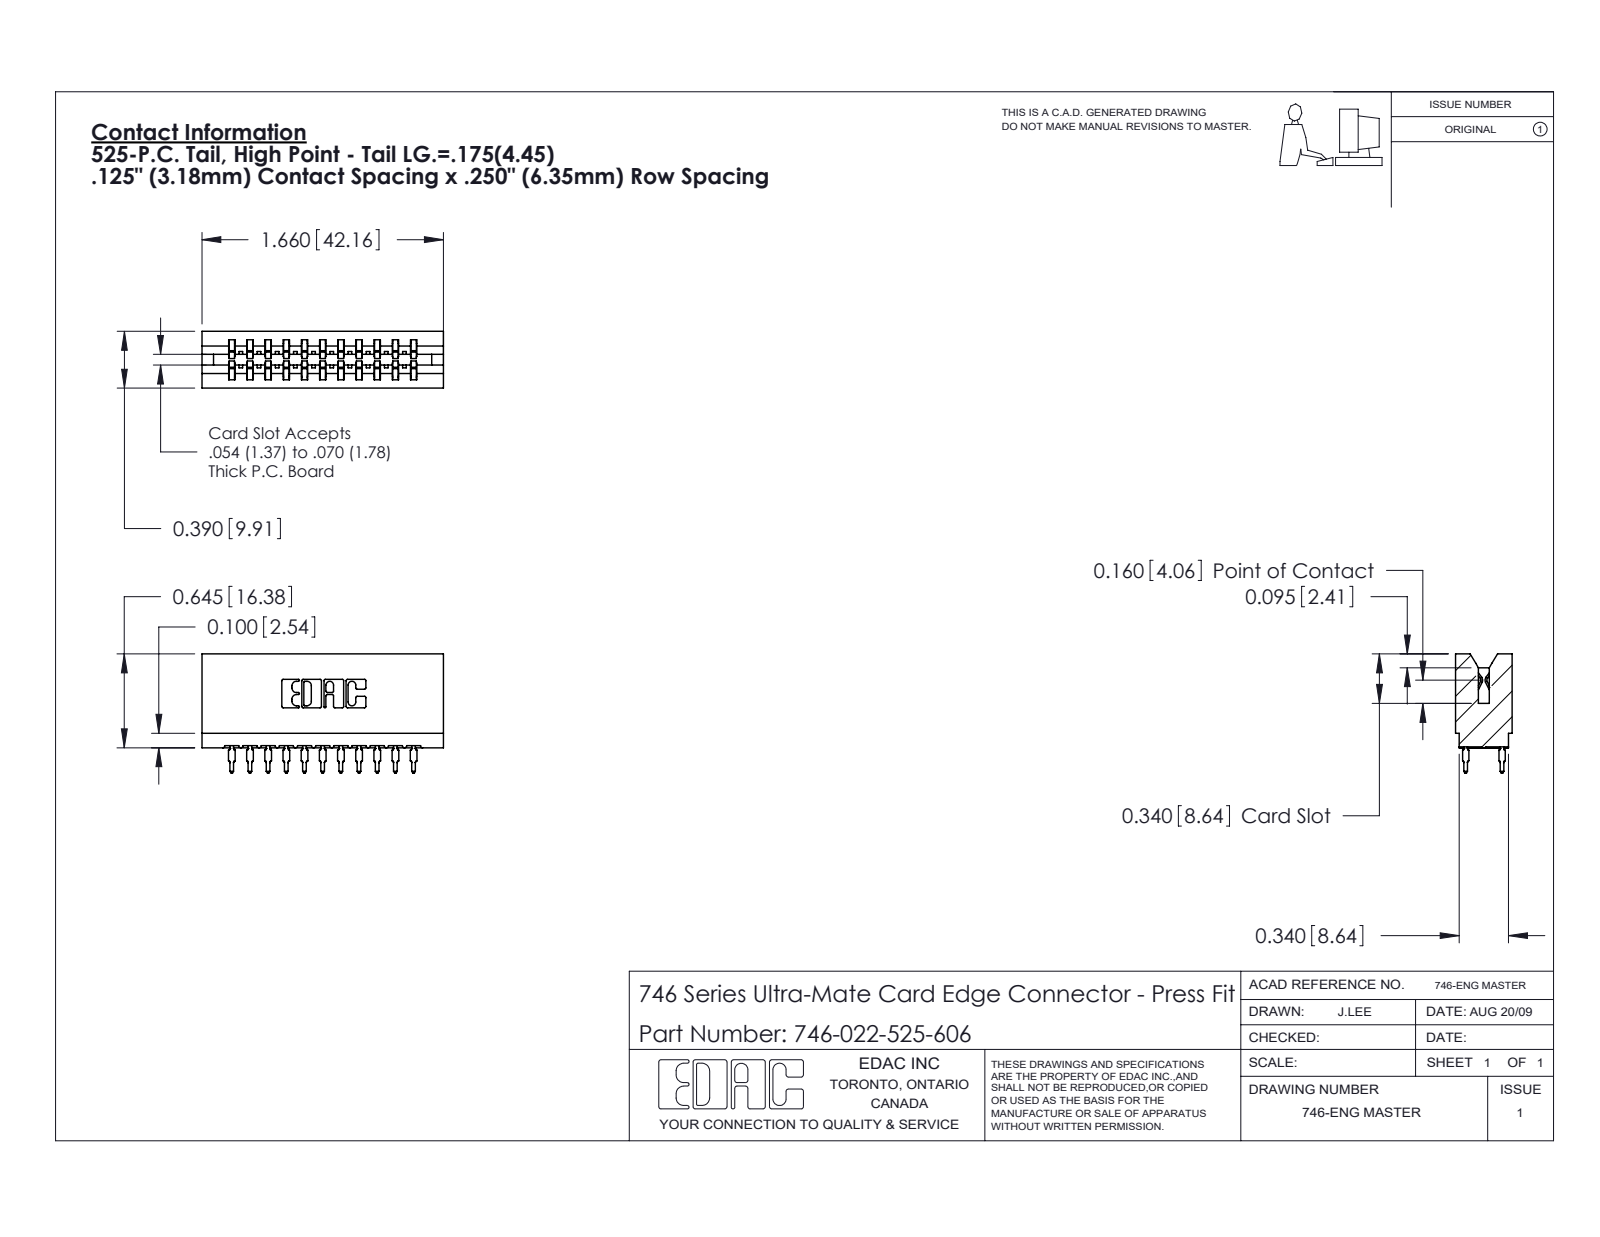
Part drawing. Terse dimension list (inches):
name: 746 Part_.340 Slot Depth - 06; 746-022-525-606; 746-292-001_525
written by: SolidWorks 2020 (CONFIG_CONTROL_DESIGN)
unit: in
bodies: 23 solids, 2067 faces (1068 planar, 427 cylindrical, 572 other)
size: 1.66 × 0.819 × 0.39
volume: 0.304 in³; area: 10.39 in²
rounds: 44× R0.021, 22× R0.01, 12× R0.015, 8× R0.005, 8× R0.011, 6× R0.007, 6× R0.031, 3× R0.026
face distances: 0.25, 0.333, 0.5, 0.057, 0.125, 0.042, 0.125, 0.292, 0.542, 0.39
